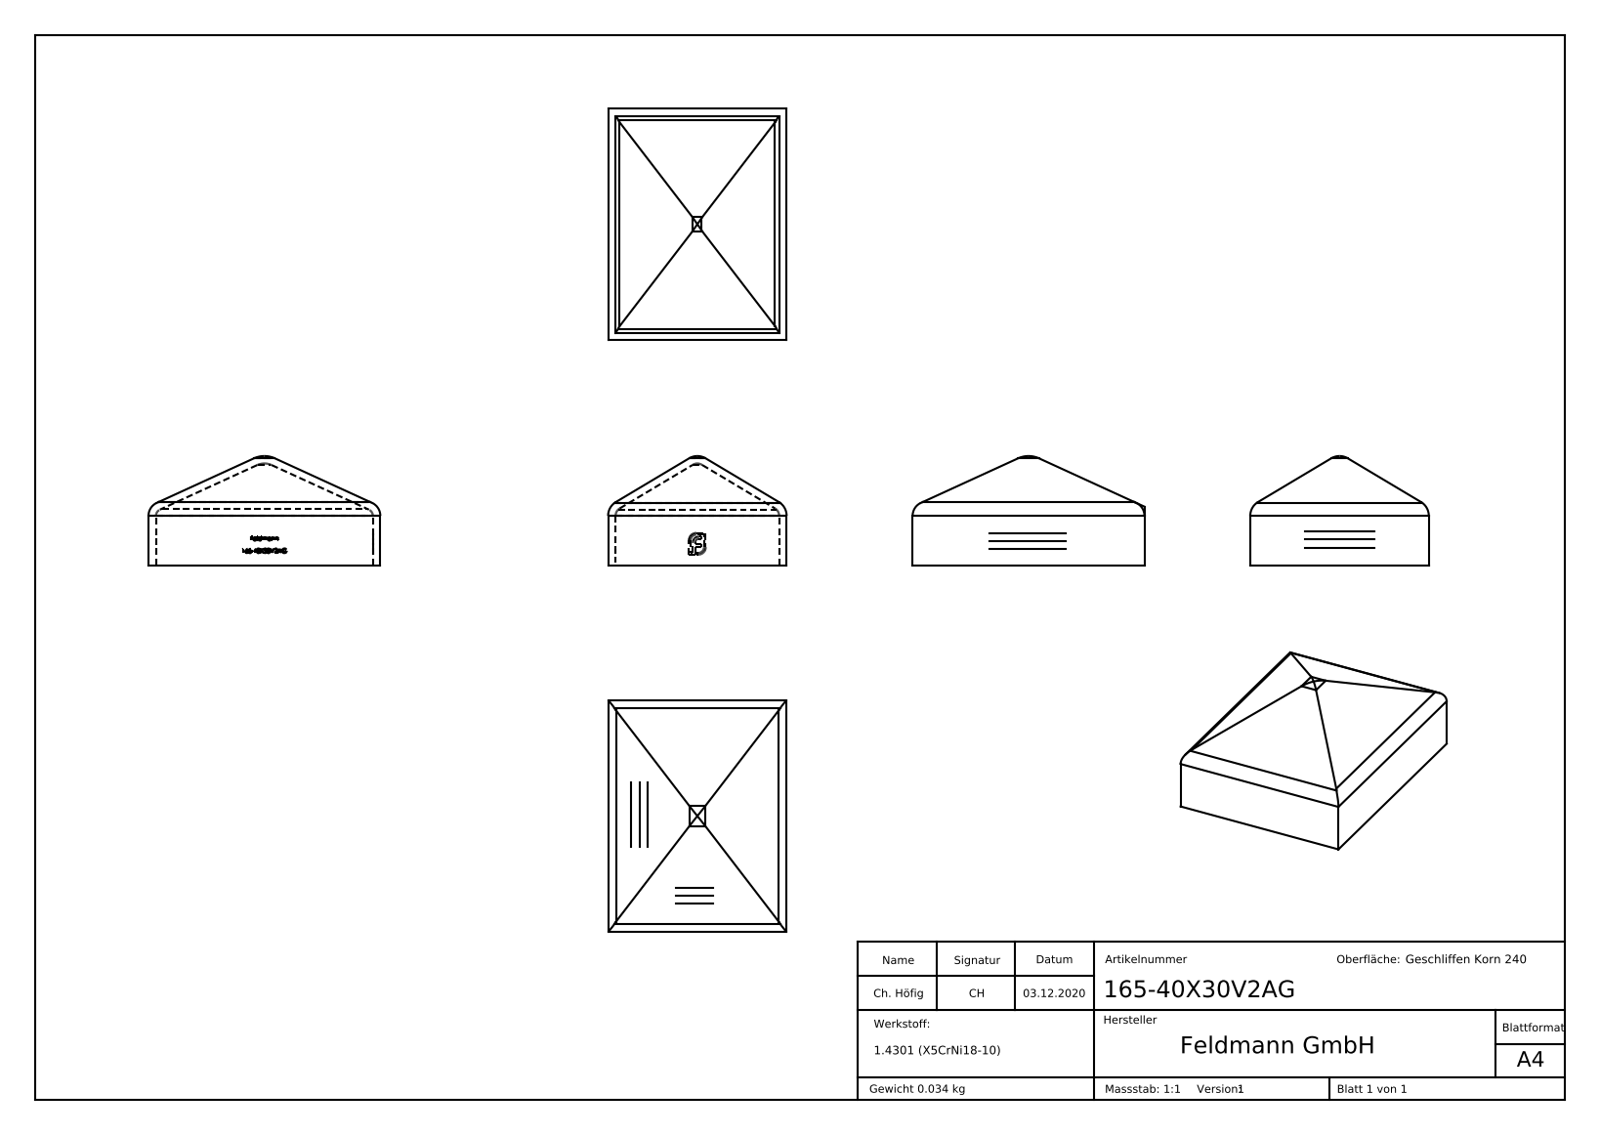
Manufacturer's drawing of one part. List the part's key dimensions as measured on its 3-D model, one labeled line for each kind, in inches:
Part name (STEP PRODUCT): 165-40X30V2AG
STEP written by: SolidWorks 2018 (CONFIG_CONTROL_DESIGN)
Units: inches
Bodies: 1 solid, 344 faces (196 planar, 16 cylindrical, 132 other)
Overall size (bounding box): 1.713 × 1.319 × 0.807
Volume: 0.261 in³ · Surface area: 9.838 in²
Partial cylindrical surfaces — rounded edges, fillets, slot ends (radius × count): R0.063 ×3, R0.118 ×3, R0.049 ×2, R0.104 ×2, R0.128 ×1, R0.183 ×1
Main face-to-face distances: 0.055, 1.264, 1.657, 1.319, 1.209, 1.713, 1.602, 0.051, 1.606, 1.661
